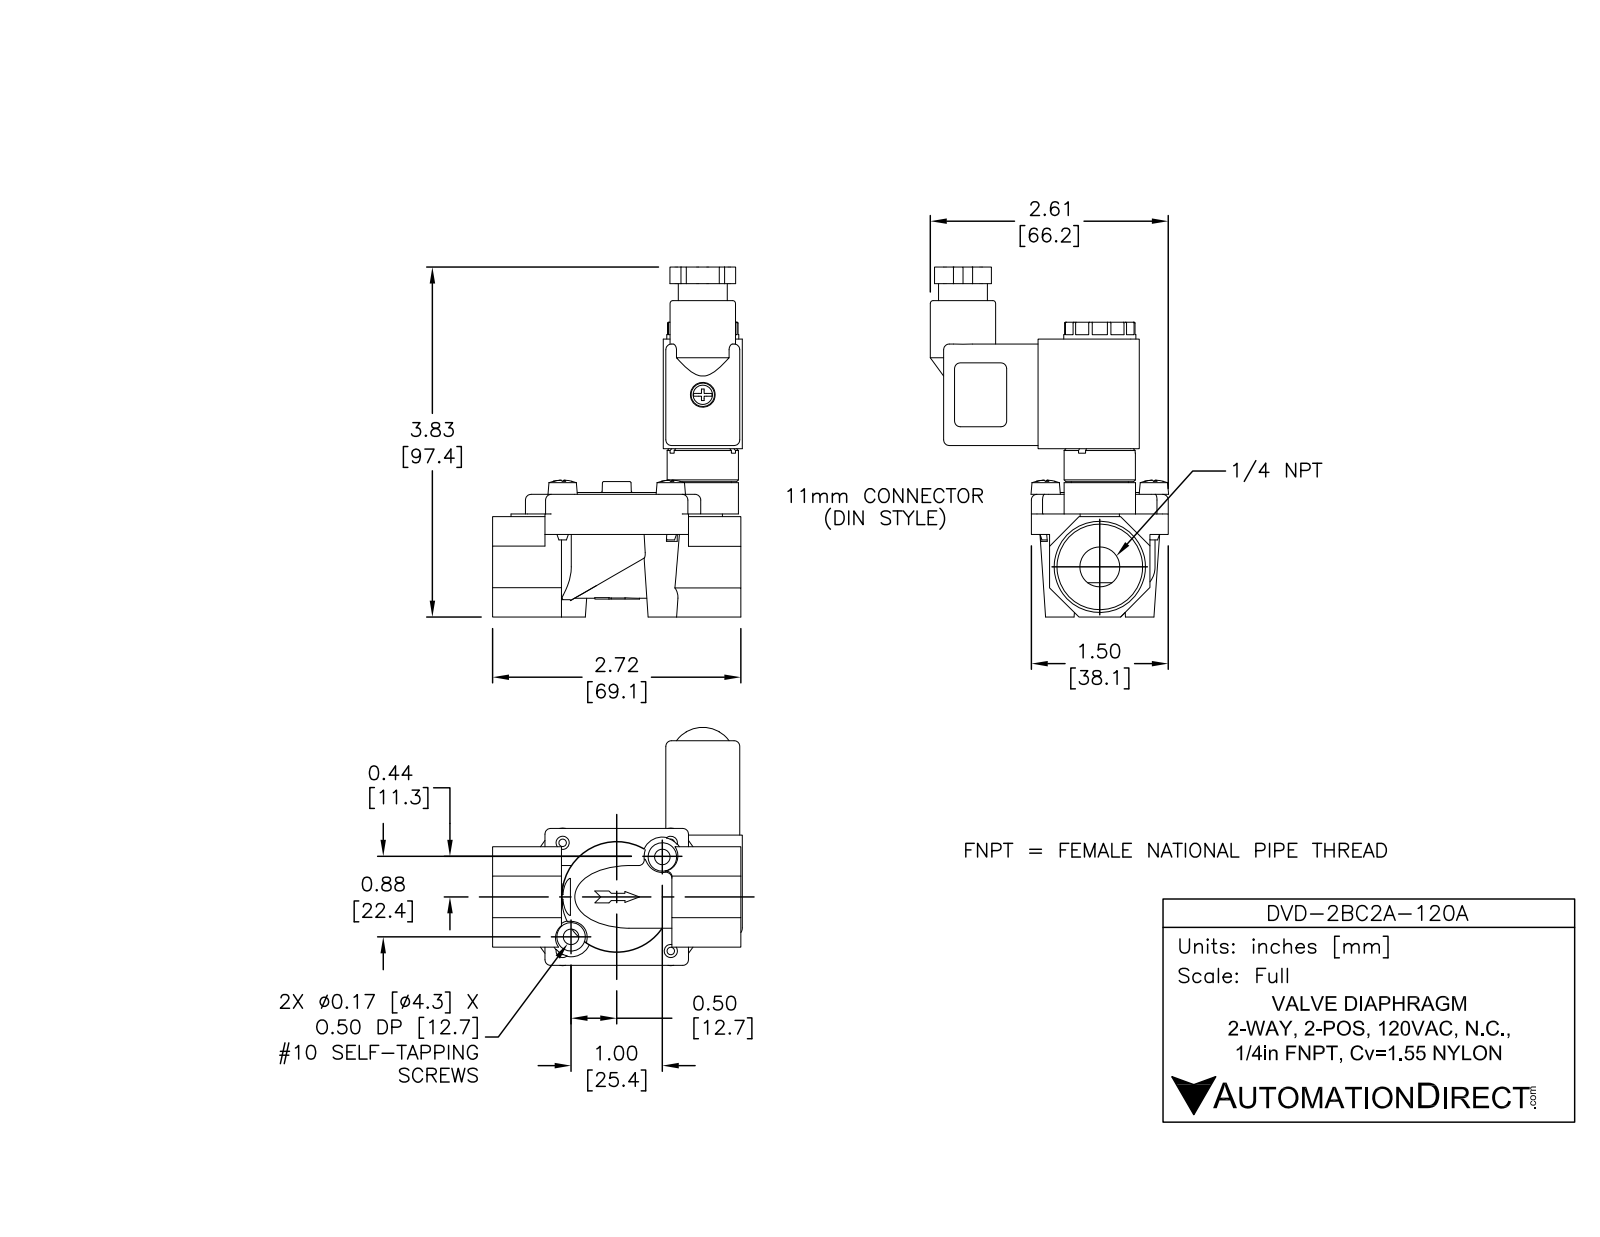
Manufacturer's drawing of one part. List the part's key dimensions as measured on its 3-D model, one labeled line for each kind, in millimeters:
Part name (STEP PRODUCT): DVD-2BC2A-120A
STEP written by: SolidWorks 2015 (AUTOMOTIVE_DESIGN)
Units: millimetres
Bodies: 11 solids, 1418 faces (715 planar, 244 cylindrical, 459 other)
Overall size (bounding box): 97.4 × 69.5 × 66.3
Volume: 69 600 mm³ · Surface area: 39 250 mm²
Round holes (diameter × count): ⌀3.7 ×4, ⌀4.2 ×4, ⌀1.5 ×2, ⌀2.4 ×2, ⌀4.3 ×2, ⌀1.6 ×1, ⌀4 ×1, ⌀4.2 ×1, ⌀6.4 ×1, ⌀6.9 ×1, ⌀7.9 ×1, ⌀8 ×1
Round bosses / shafts (diameter × count): ⌀4.7 ×4, ⌀3.2 ×4, ⌀15.9 ×2, ⌀34.9 ×1, ⌀20.1 ×1, ⌀19.9 ×1, ⌀19.8 ×1, ⌀18.2 ×1
Partial cylindrical surfaces — rounded edges, fillets, slot ends (radius × count): R0.3 ×24, R1.6 ×24, R4 ×12, R1.1 ×3, R2.4 ×2, R5.5 ×2, R7.7 ×1, R8.7 ×1
Main face-to-face distances: 1.3, 27.9, 22, 19.3, 5.1, 33, 20, 2, 2, 18
Hole centre spacings: 21.3, 30.1, 4.6, 16.9, 17.5, 26.3, 28, 38.2
